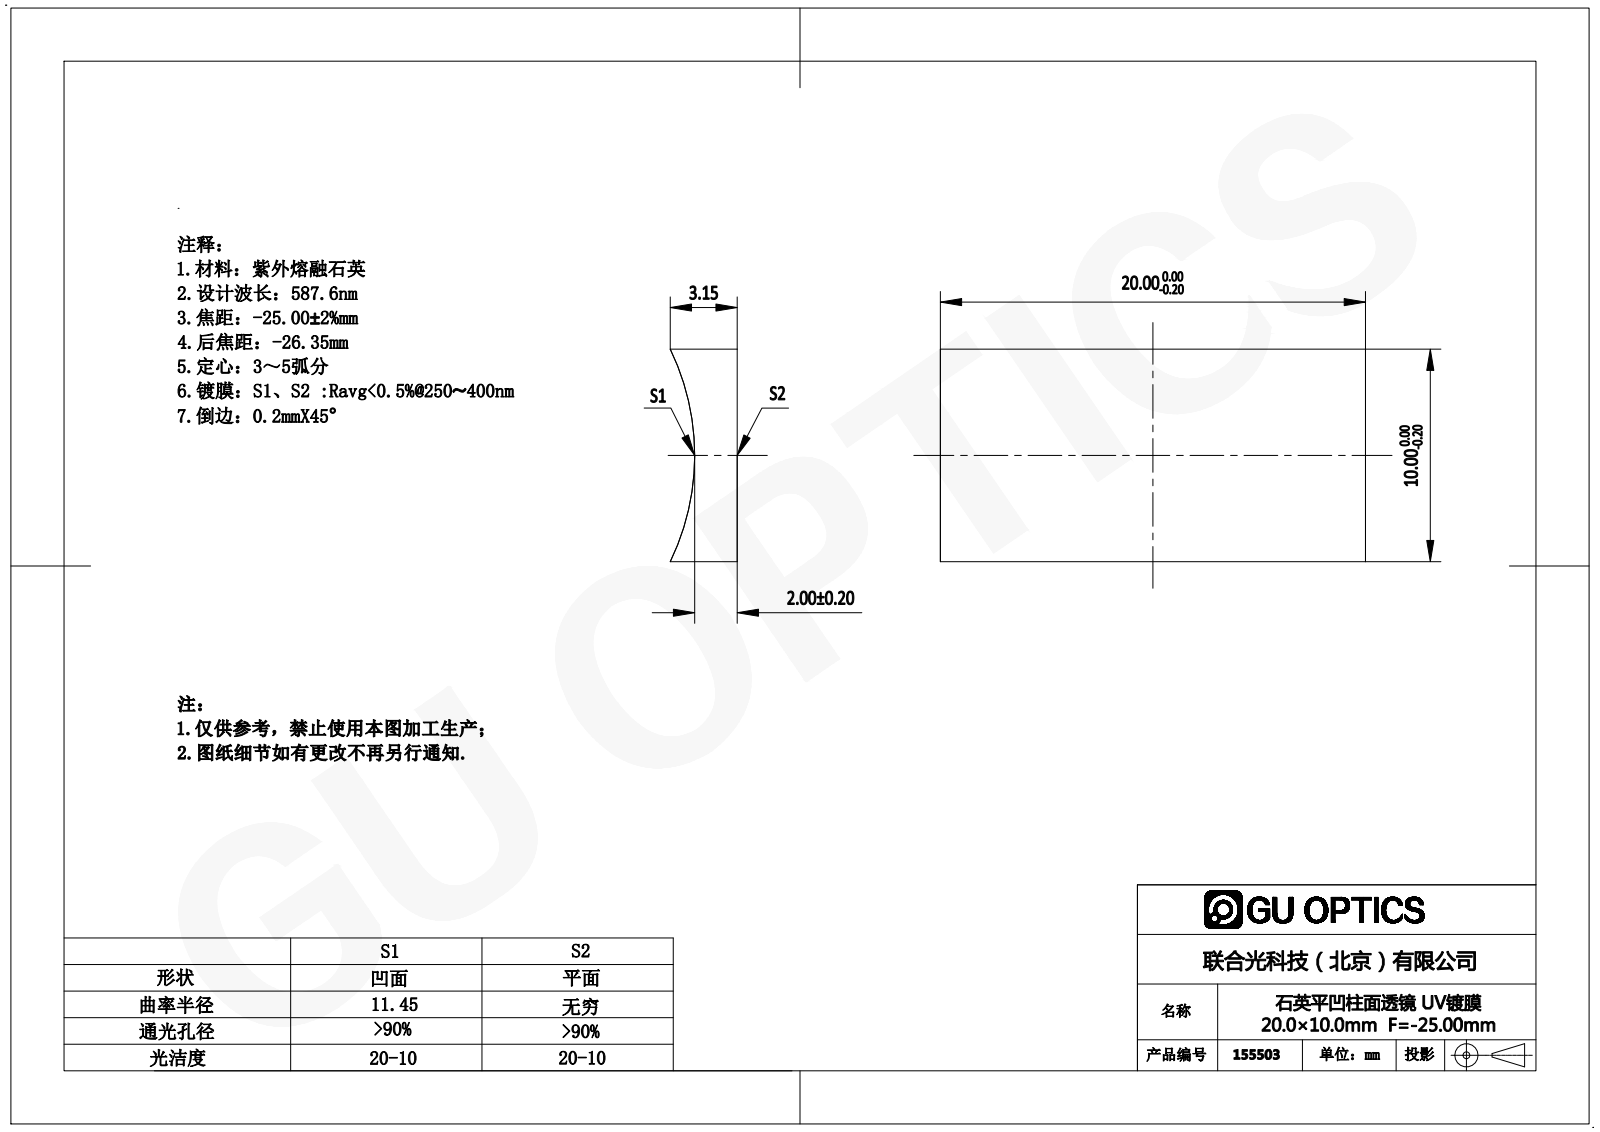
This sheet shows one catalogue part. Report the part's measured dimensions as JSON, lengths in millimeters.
{"part_name": "155477", "step_written_by": "SolidWorks 2016 (AUTOMOTIVE_DESIGN)", "units": "millimeters", "bodies": {"solids": 1, "faces": 6, "planar": 5, "cylindrical": 1, "other": 0}, "overall_size": [20, 10, 3.15], "volume_mm3": 475, "surface_area_mm2": 580, "partial_cylinders_radius": [[11.45, 1]], "face_to_face_distances": [10, 20]}
